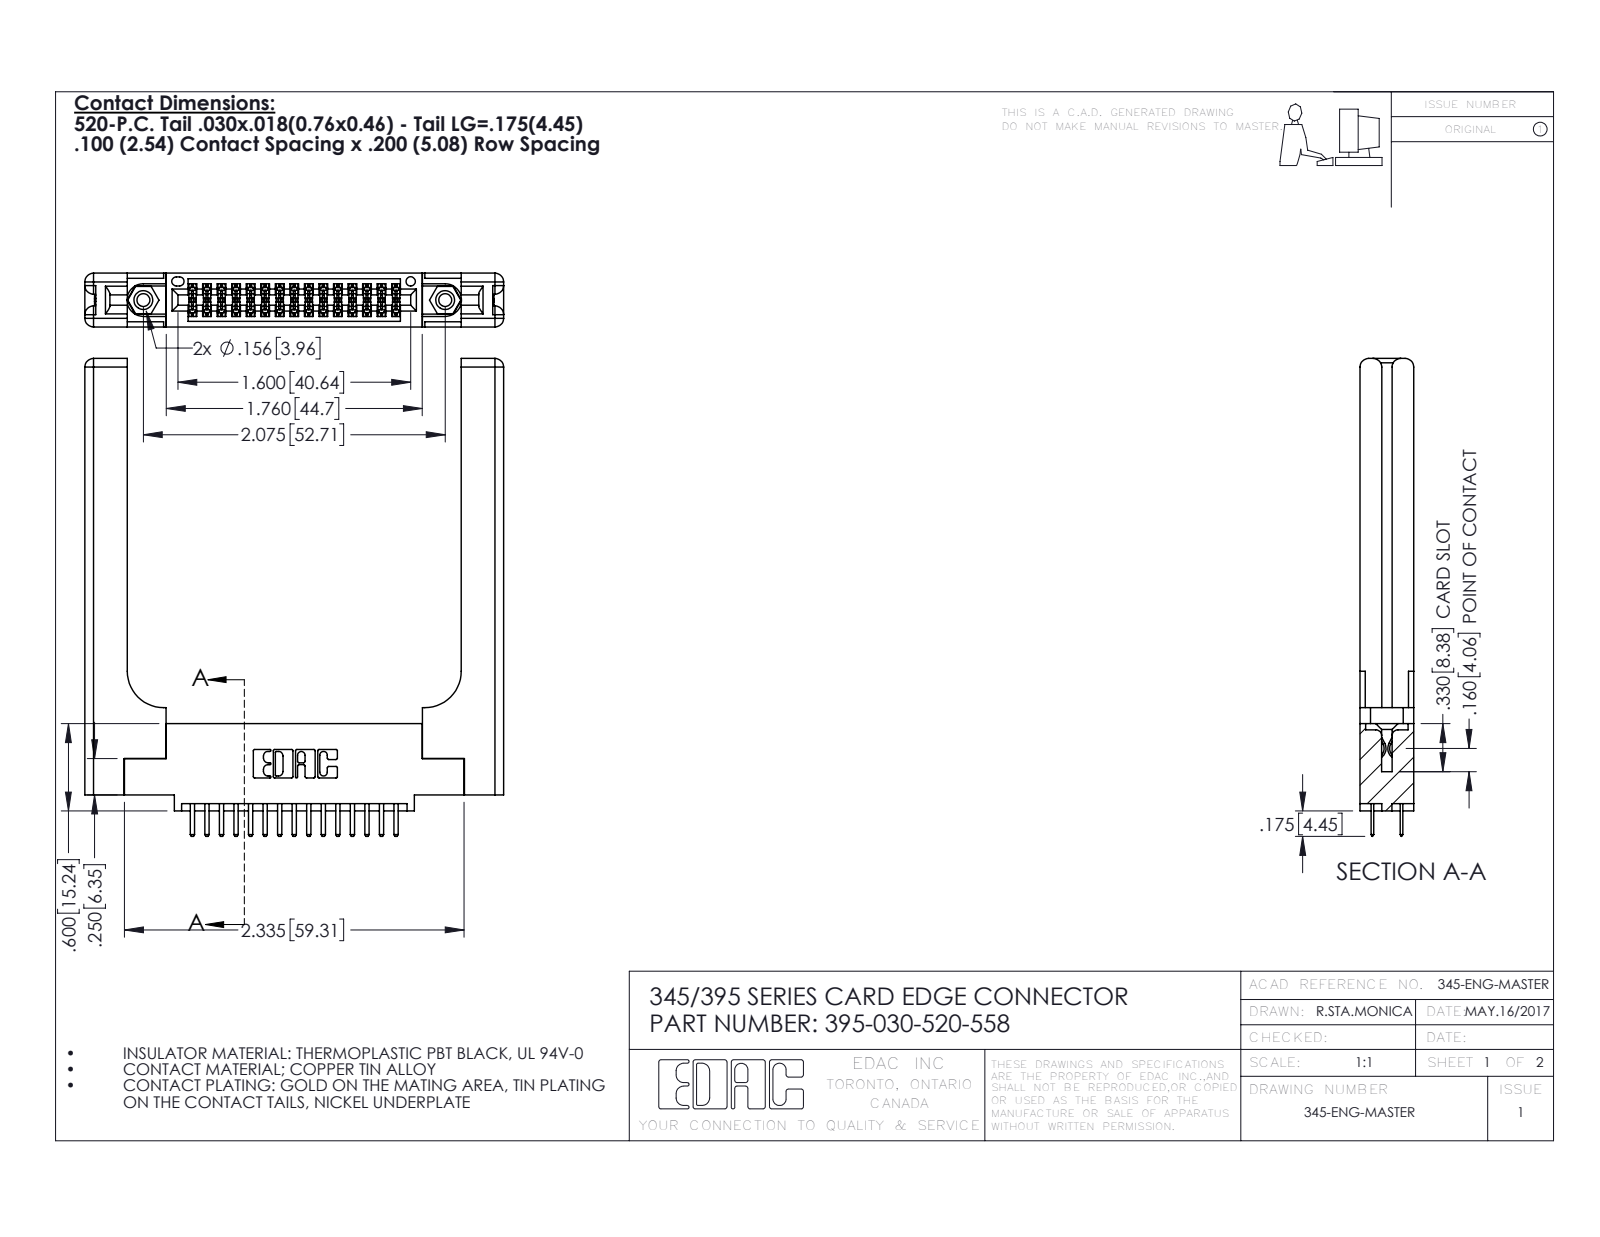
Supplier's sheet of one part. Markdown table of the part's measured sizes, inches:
| quantity | value |
| --- | --- |
| part name | 395-030-520-558; 345-292-001_345-293-120; 345-220-058_345-220-058; 345 Part_0.110 Offset - 0.156 Dia-TH (+1 more) |
| STEP written by | SolidWorks 2016 (CONFIG_CONTROL_DESIGN) |
| units | inches |
| bodies | 35 solids, 2006 faces (1282 planar, 664 cylindrical, 60 other) |
| overall size | 3.285 × 2.879 × 0.37 |
| volume | 0.93 in³ |
| surface area | 22.63 in² |
| round holes (diameter × count) | 0.089 × 2, 0.125 × 2, 0.156 × 2, 0.064 × 1 |
| round bosses / shafts (diameter × count) | 0.155 × 2 |
| partial cylindrical surfaces (radius × count) | 0.006 × 45, 0.01 × 34, 0.01 × 22, 0.06 × 16, 0.007 × 6, 0.031 × 6, 0.026 × 3, 0.014 × 2 |
| main face-to-face distances | 0.37, 0.072, 0.298, 0.15, 0.22, 0.077, 0.148, 0.2, 0.225, 0.098 |
| hole center spacings | 0.27, 1.842, 2.075 |
